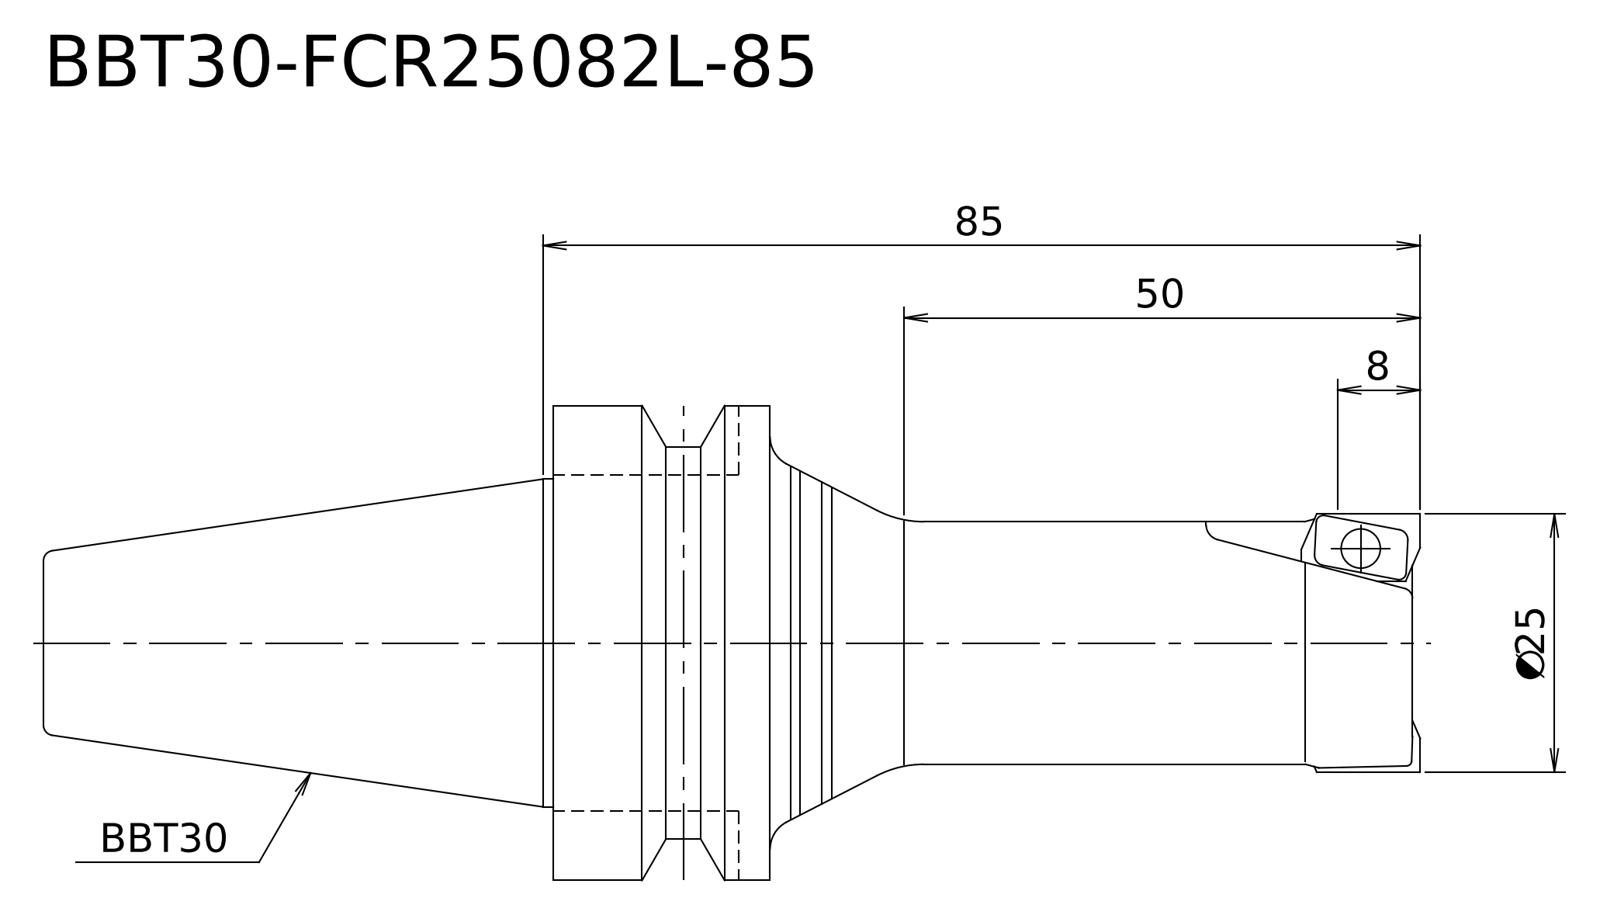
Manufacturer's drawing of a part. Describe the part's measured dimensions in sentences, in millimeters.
Its 3-D file was written by "Kubotek KeyCreator V8.5.1 (14335) (CONFIG_CONTROL_DESIGN)". It is 1 solid with 17 faces: 4 planar, 6 cylindrical and 7 other. Overall it measures 133.4 by 46 by 46 millimeters. Its volume is 88 098 cubic millimeters and its surface area 14 667 square millimeters. Round bosses or shafts: 1 of diameter 46, 1 of diameter 38, 1 of diameter 31.75, 1 of diameter 25, 1 of diameter 23.5. The main face-to-face distances are 84, 63, 21, 133.4, 70.4, 49.4.
